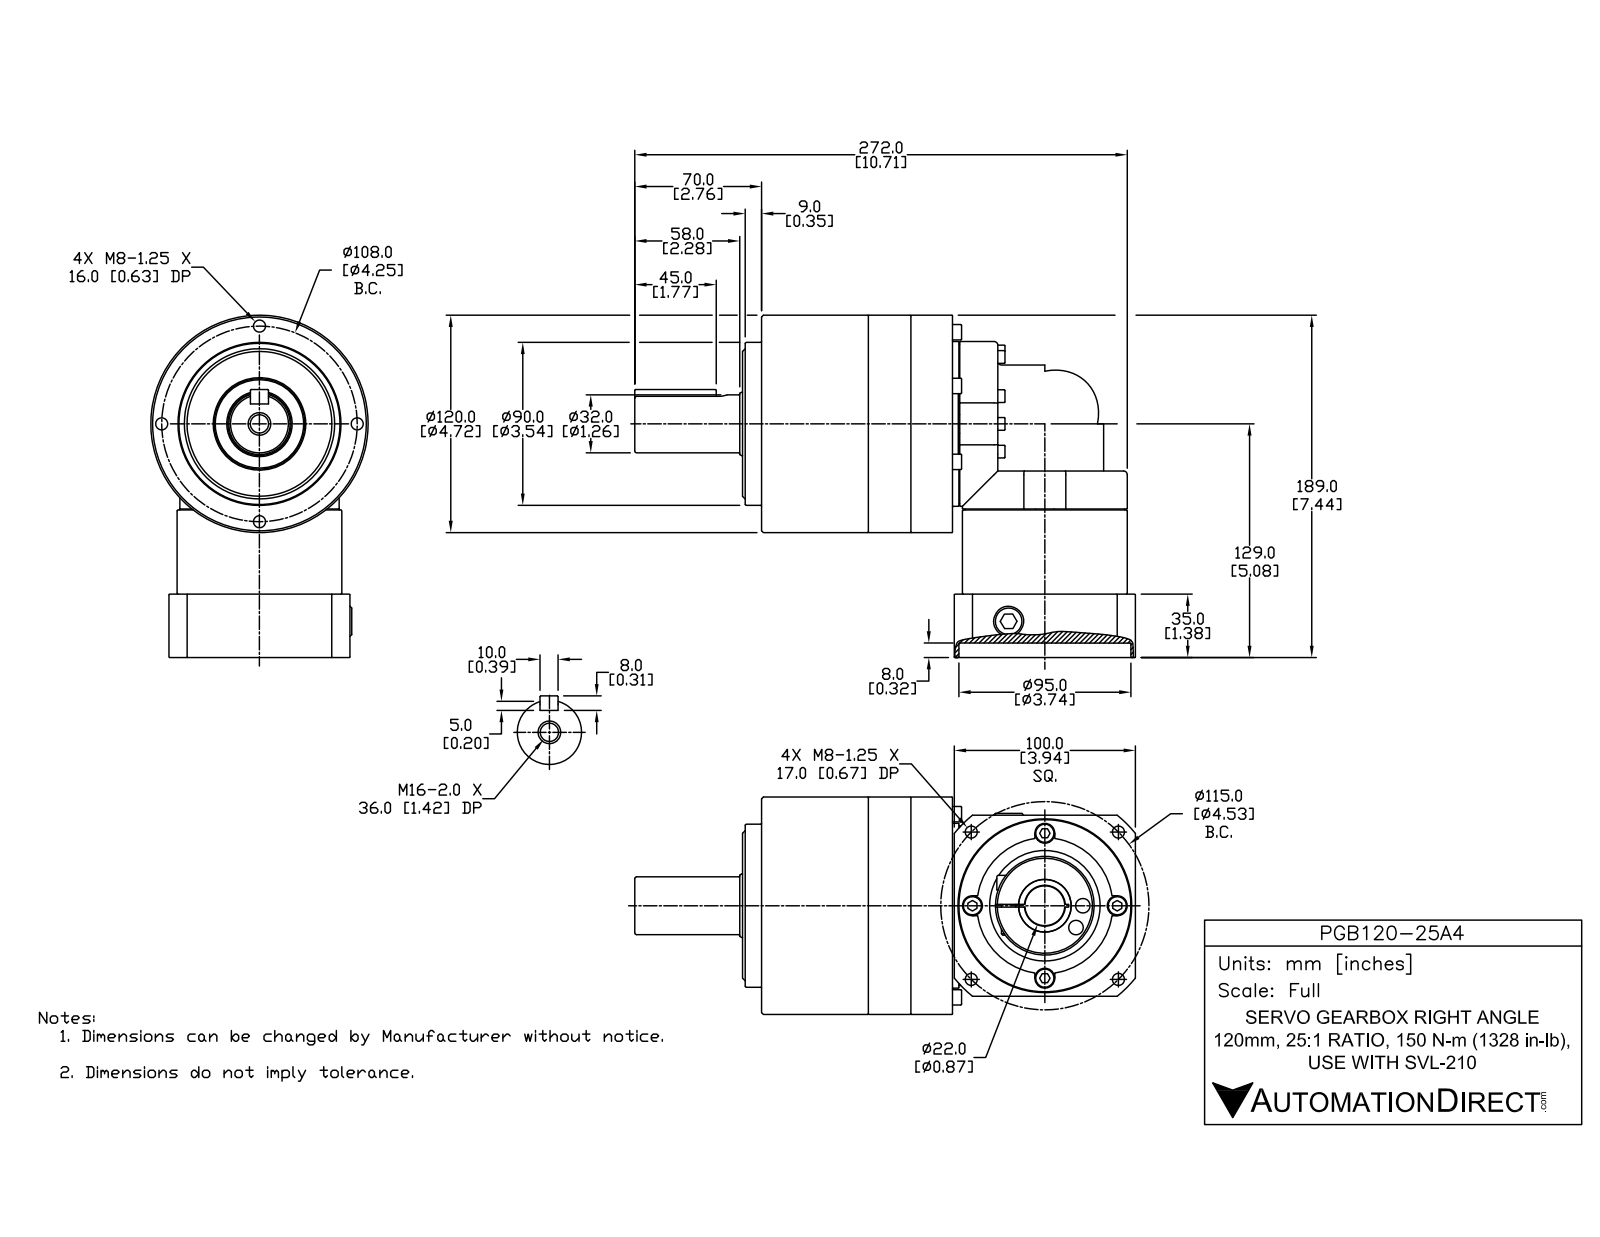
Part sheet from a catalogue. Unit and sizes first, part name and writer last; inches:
Units: inches
Overall size (bounding box): 10.886 × 7.441 × 4.724
Round holes (diameter × count): ⌀0.262 ×8, ⌀0.217 ×6, ⌀0.433 ×4, ⌀0.315 ×2, ⌀0.346 ×1, ⌀0.398 ×1, ⌀0.561 ×1, ⌀0.866 ×1, ⌀2.402 ×1, ⌀2.953 ×1, ⌀3.74 ×1
Round bosses / shafts (diameter × count): ⌀0.276 ×9, ⌀0.335 ×6, ⌀0.197 ×6, ⌀0.394 ×4, ⌀3.583 ×2, ⌀3.465 ×2, ⌀4.724 ×1, ⌀3.543 ×1
Partial cylindrical surfaces — rounded edges, fillets, slot ends (radius × count): R0.079 ×6, R1.28 ×2, R0.131 ×1, R0.197 ×1, R0.276 ×1, R2.52 ×1
Main face-to-face distances: 3.937, 4.154, 0.413, 4.567, 0.039, 4.606, 3.976, 8.13, 8.543, 4.193
Hole centre spacings: 1.601, 3.556, 0.836, 2.156, 2.379, 3.56, 4.199, 1.65
Volume: 137.2 in³ · Surface area: 249.4 in²
Bodies: 1 solid, 640 faces (271 planar, 166 cylindrical, 203 other)
Part name (STEP PRODUCT): PGB120-25A4
STEP written by: SolidWorks 2014 (AUTOMOTIVE_DESIGN)
